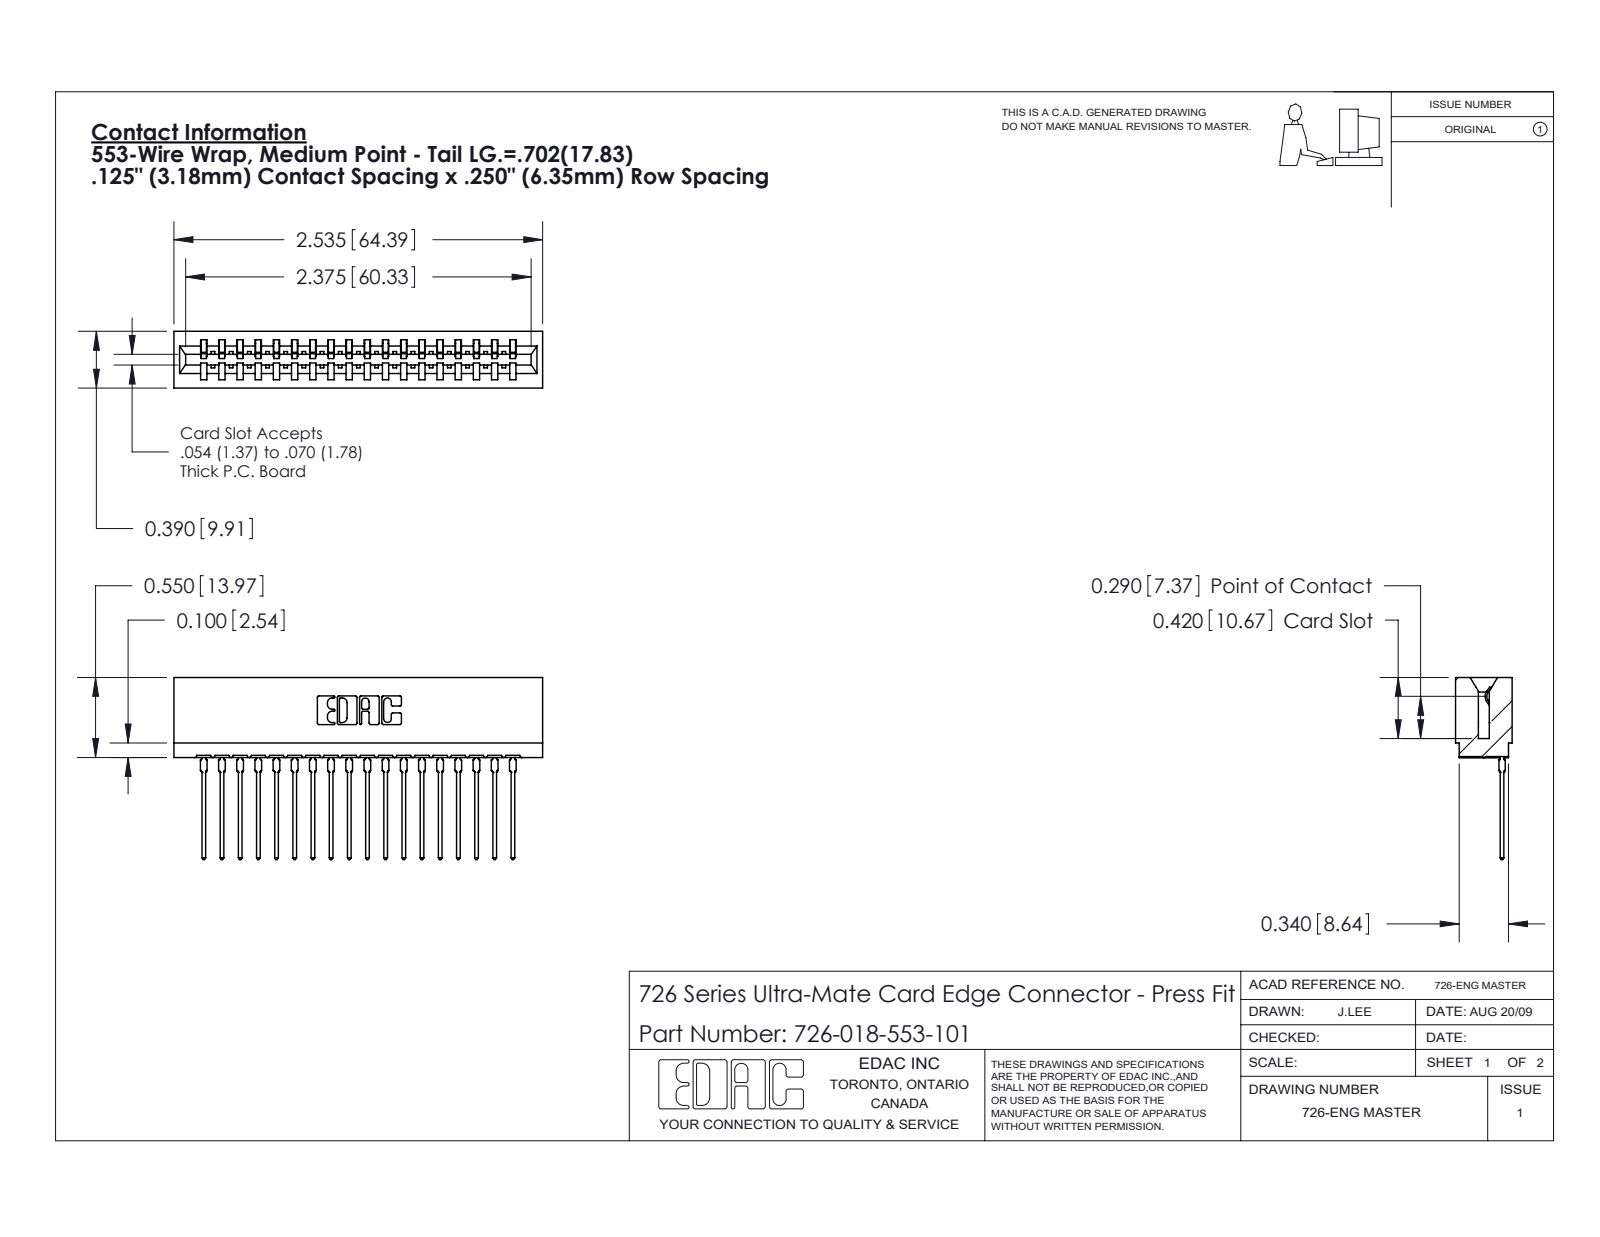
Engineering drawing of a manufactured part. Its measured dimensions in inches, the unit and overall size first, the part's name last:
Units: inches
Overall size (bounding box): 2.535 × 1.251 × 0.39
Partial cylindrical surfaces — rounded edges, fillets, slot ends (radius × count): R0.021 ×36, R0.01 ×22, R0.015 ×19, R0.007 ×6, R0.031 ×6, R0.005 ×4, R0.011 ×4, R0.026 ×3
Main face-to-face distances: 0.057, 0.333, 0.25, 0.39, 0.025, 0.307, 0.083, 0.75, 0.5, 0.125
Volume: 0.363 in³ · Surface area: 14.05 in²
Bodies: 19 solids, 2041 faces (1189 planar, 384 cylindrical, 468 other)
Part name (STEP PRODUCT): 726-018-553-101; 746-292-001_553; 726 Part_.515 Slot Depth - 01
STEP written by: SolidWorks 2020 (CONFIG_CONTROL_DESIGN)
